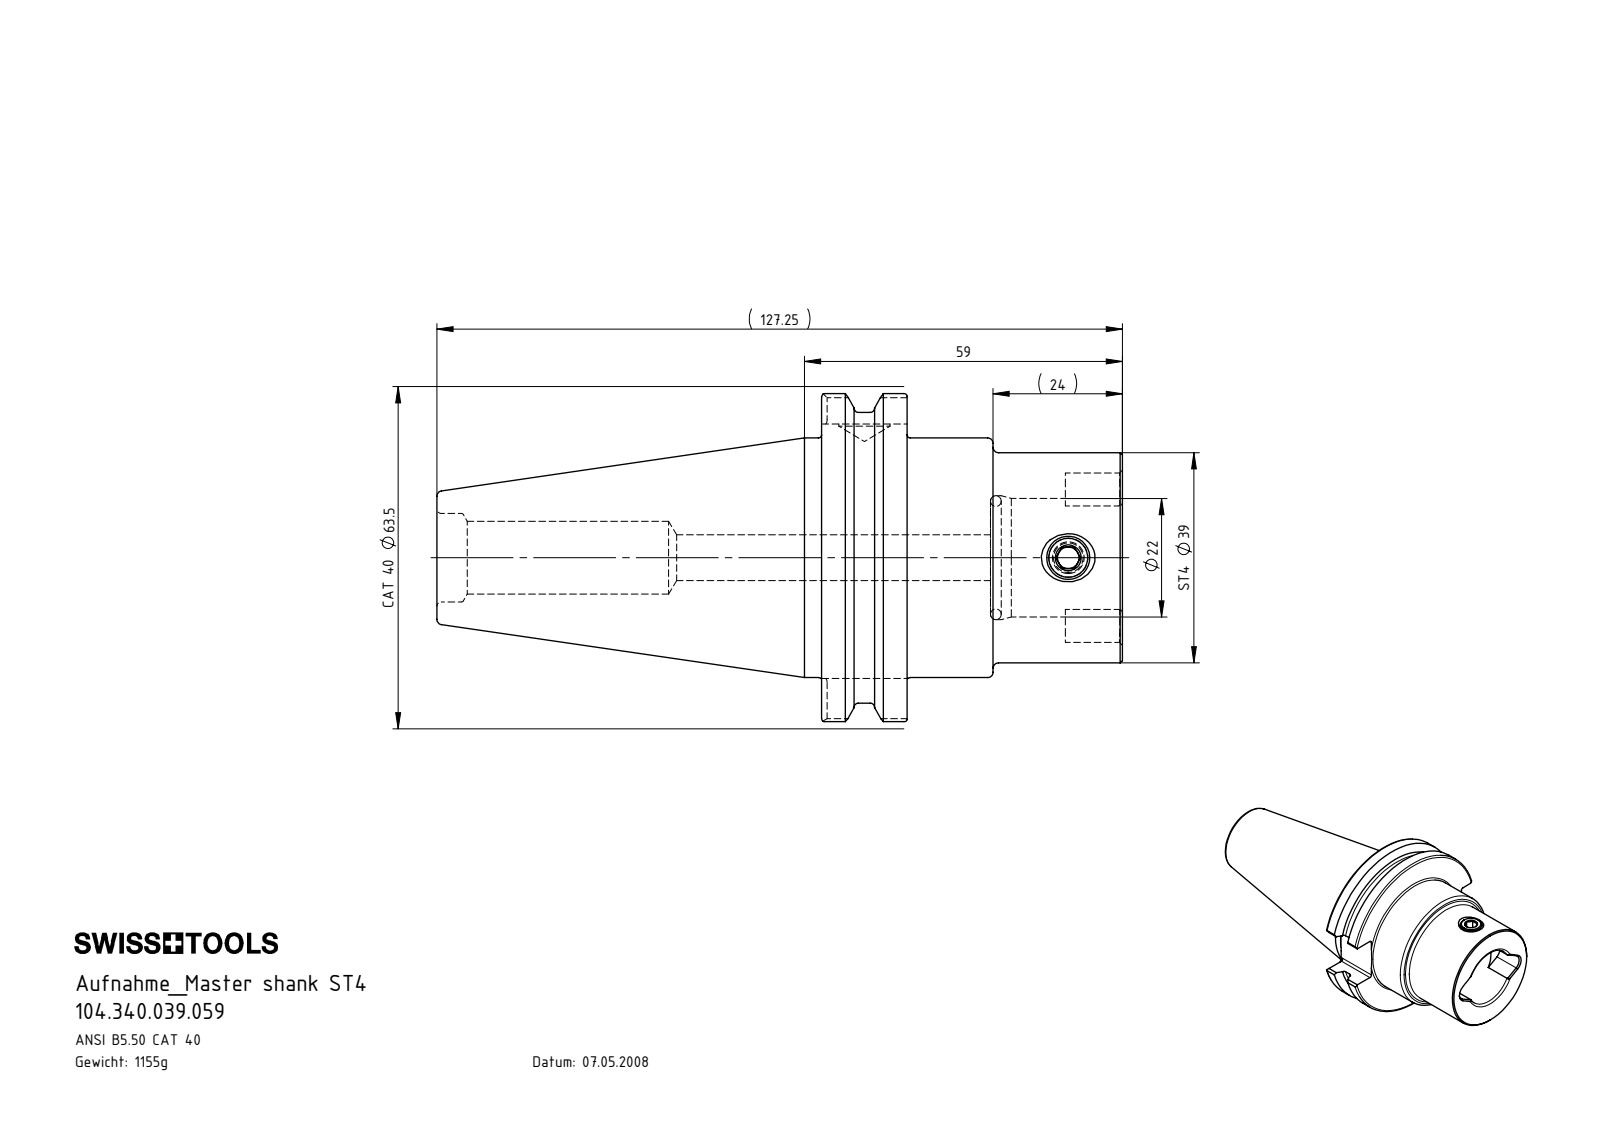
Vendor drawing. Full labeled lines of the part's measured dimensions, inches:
Part name (STEP PRODUCT): ST4-ER1.001.011_A; CT4-ST4.K01.059_A; DIN 3771 - 19x1.5_19x2; CT4-ST4.K01.059
STEP written by: SolidWorks 2015 (CONFIG_CONTROL_DESIGN)
Units: inches
Bodies: 3 solids, 144 faces (44 planar, 39 cylindrical, 61 other)
Overall size (bounding box): 5.01 × 2.5 × 2.396
Volume: 8.995 in³ · Surface area: 42.7 in²
Round holes (diameter × count): ⌀0.285 ×1, ⌀0.335 ×1, ⌀0.374 ×1, ⌀0.531 ×1, ⌀0.647 ×1, ⌀0.866 ×1, ⌀0.906 ×1
Round bosses / shafts (diameter × count): ⌀2.5 ×1, ⌀2.219 ×1, ⌀1.75 ×1, ⌀1.535 ×1, ⌀0.315 ×1
Partial cylindrical surfaces — rounded edges, fillets, slot ends (radius × count): R0.031 ×8, R0.126 ×2
Main face-to-face distances: 0.625, 2.198, 1.573, 1.233, 0.608, 0.965, 1.858, 2.812, 3.437, 4.045
